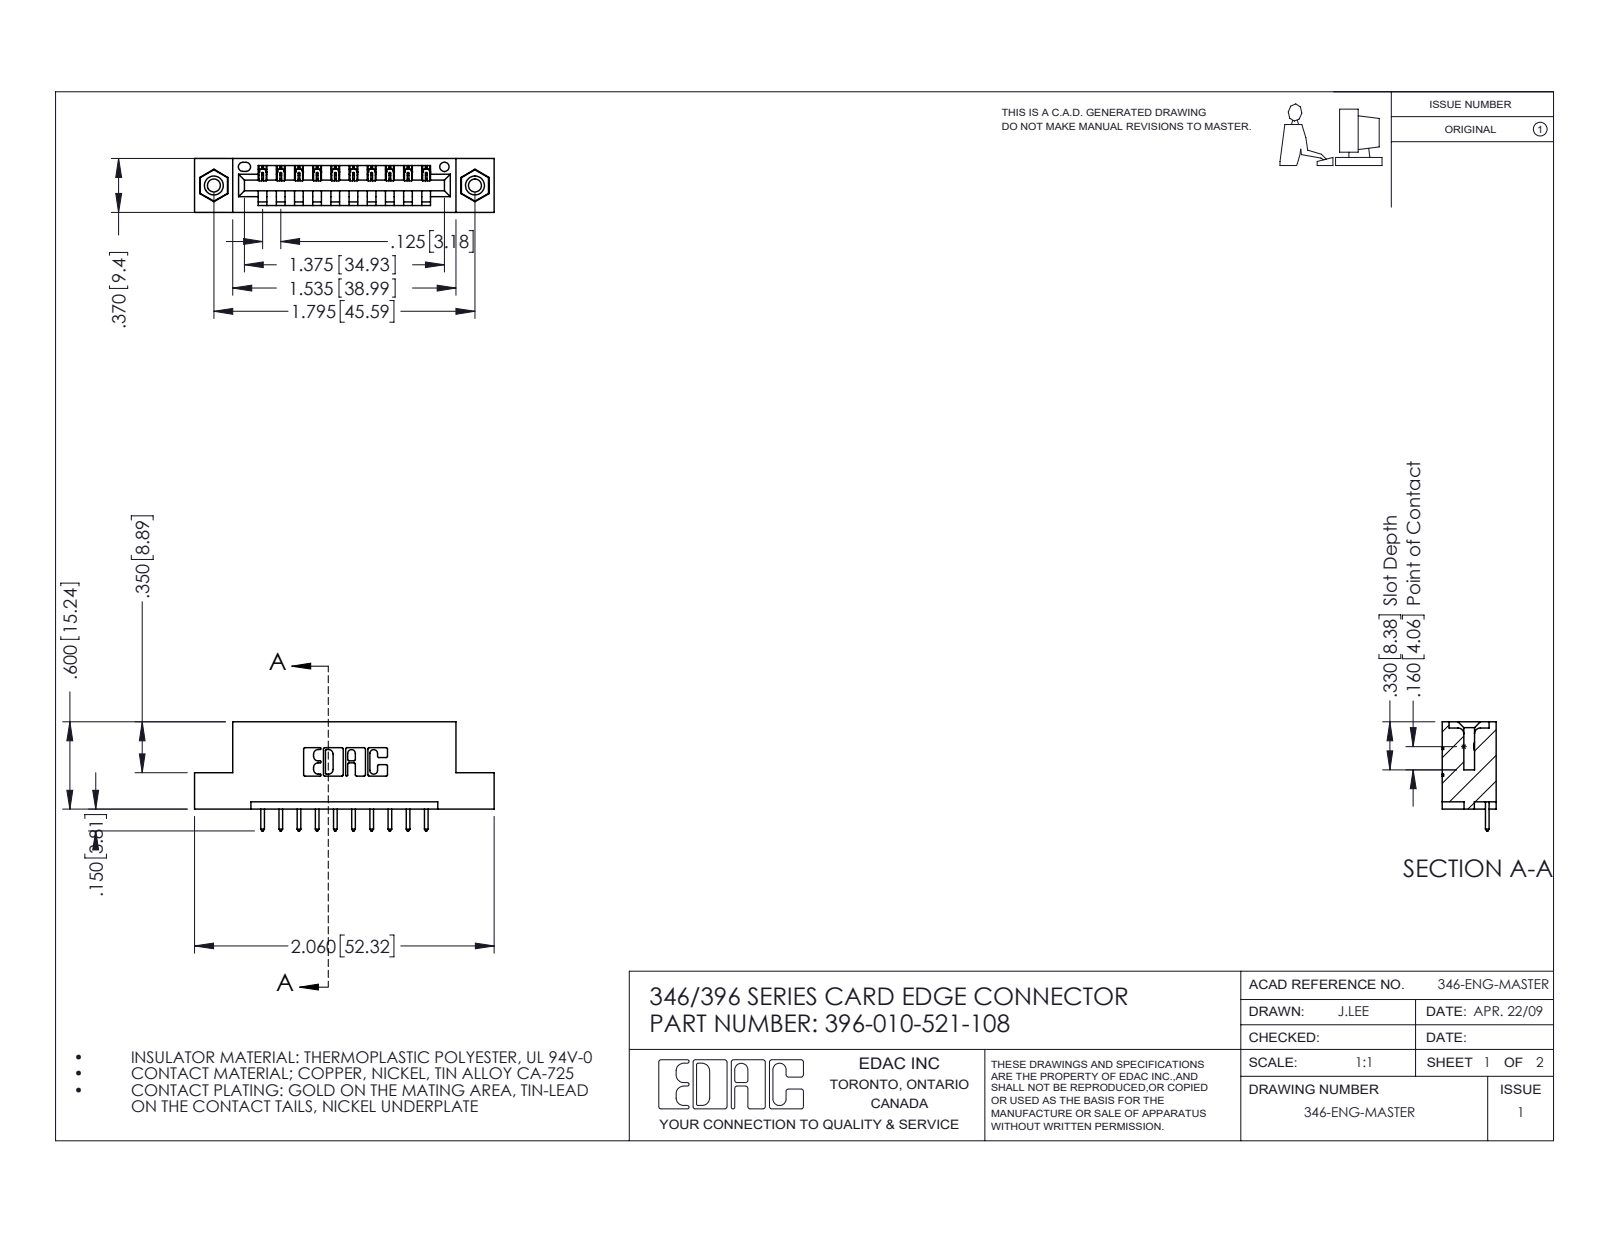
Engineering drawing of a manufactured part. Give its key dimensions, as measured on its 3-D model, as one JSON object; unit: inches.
{"part_name": "346 Part_Flush Mounting Lugs - 0.156 Dia-TI; 345-250-001_345-250-003-102; 396-010-521-108; 345-292-001_345-293-121", "step_written_by": "SolidWorks 2016 (CONFIG_CONTROL_DESIGN)", "units": "inches", "bodies": {"solids": 13, "faces": 762, "planar": 508, "cylindrical": 238, "other": 16}, "overall_size": [2.06, 0.75, 0.37], "volume_in3": 0.29, "surface_area_in2": 8.531, "round_holes": [[0.089, 2], [0.125, 2], [0.156, 2], [0.064, 1]], "round_bosses_or_shafts": [[0.155, 2]], "partial_cylinders_radius": [[0.01, 22], [0.006, 20], [0.01, 20], [0.007, 6], [0.031, 6], [0.026, 3], [0.031, 2], [0.04, 2]], "face_to_face_distances": [0.25, 0.37, 0.048, 0.322, 0.148, 0.222, 0.1, 0.174, 0.072, 0.298], "hole_center_spacings": [0.246, 1.59, 1.795]}
